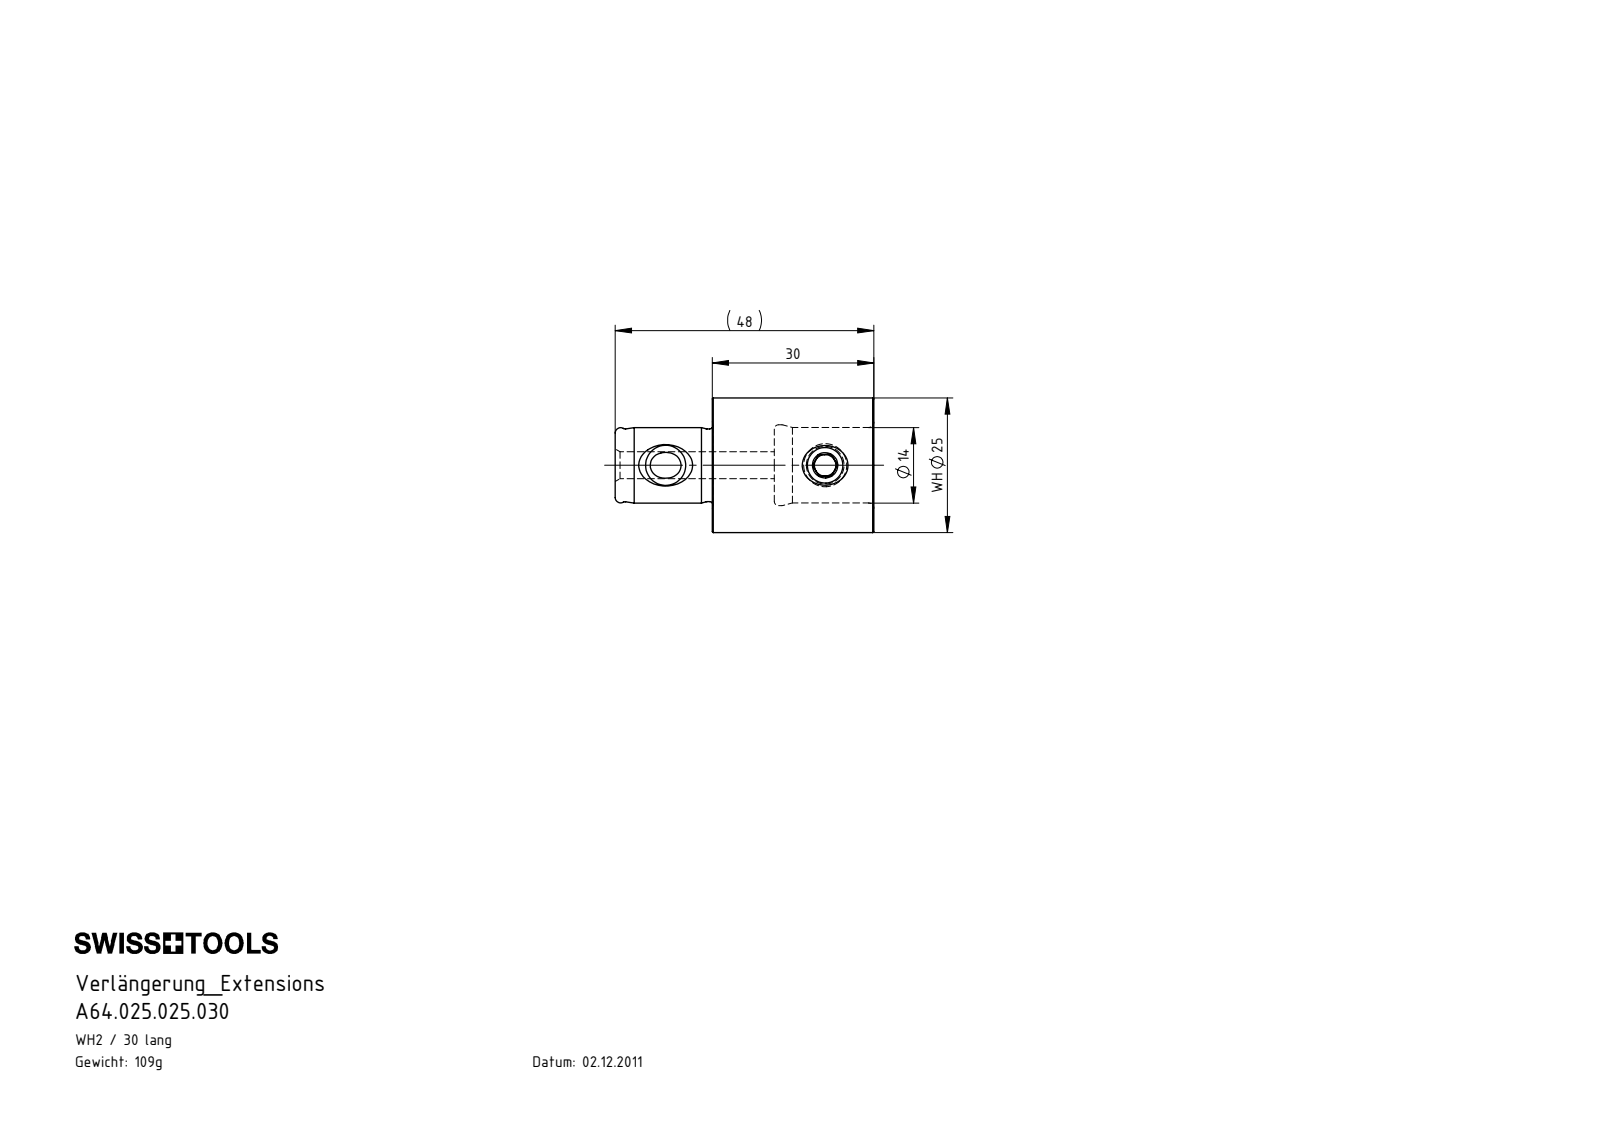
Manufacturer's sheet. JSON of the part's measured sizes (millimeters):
{"part_name": "WH2-ER1.001.008_A; WH2-WH2.001.030; WH2-WH2.001.030_A", "step_written_by": "SolidWorks 2015 (AUTOMOTIVE_DESIGN)", "units": "millimeters", "bodies": {"solids": 2, "faces": 71, "planar": 13, "cylindrical": 16, "other": 42}, "overall_size": [48, 25, 25], "volume_mm3": 13868, "surface_area_mm2": 5712, "round_holes": [[5, 1], [7, 1], [14, 1], [15, 1]], "round_bosses_or_shafts": [[25, 1], [13.5, 1], [8, 1]], "face_to_face_distances": [30, 11.5, 18.5, 18, 29.5, 48, 4, 8.5, 3.5, 5]}
